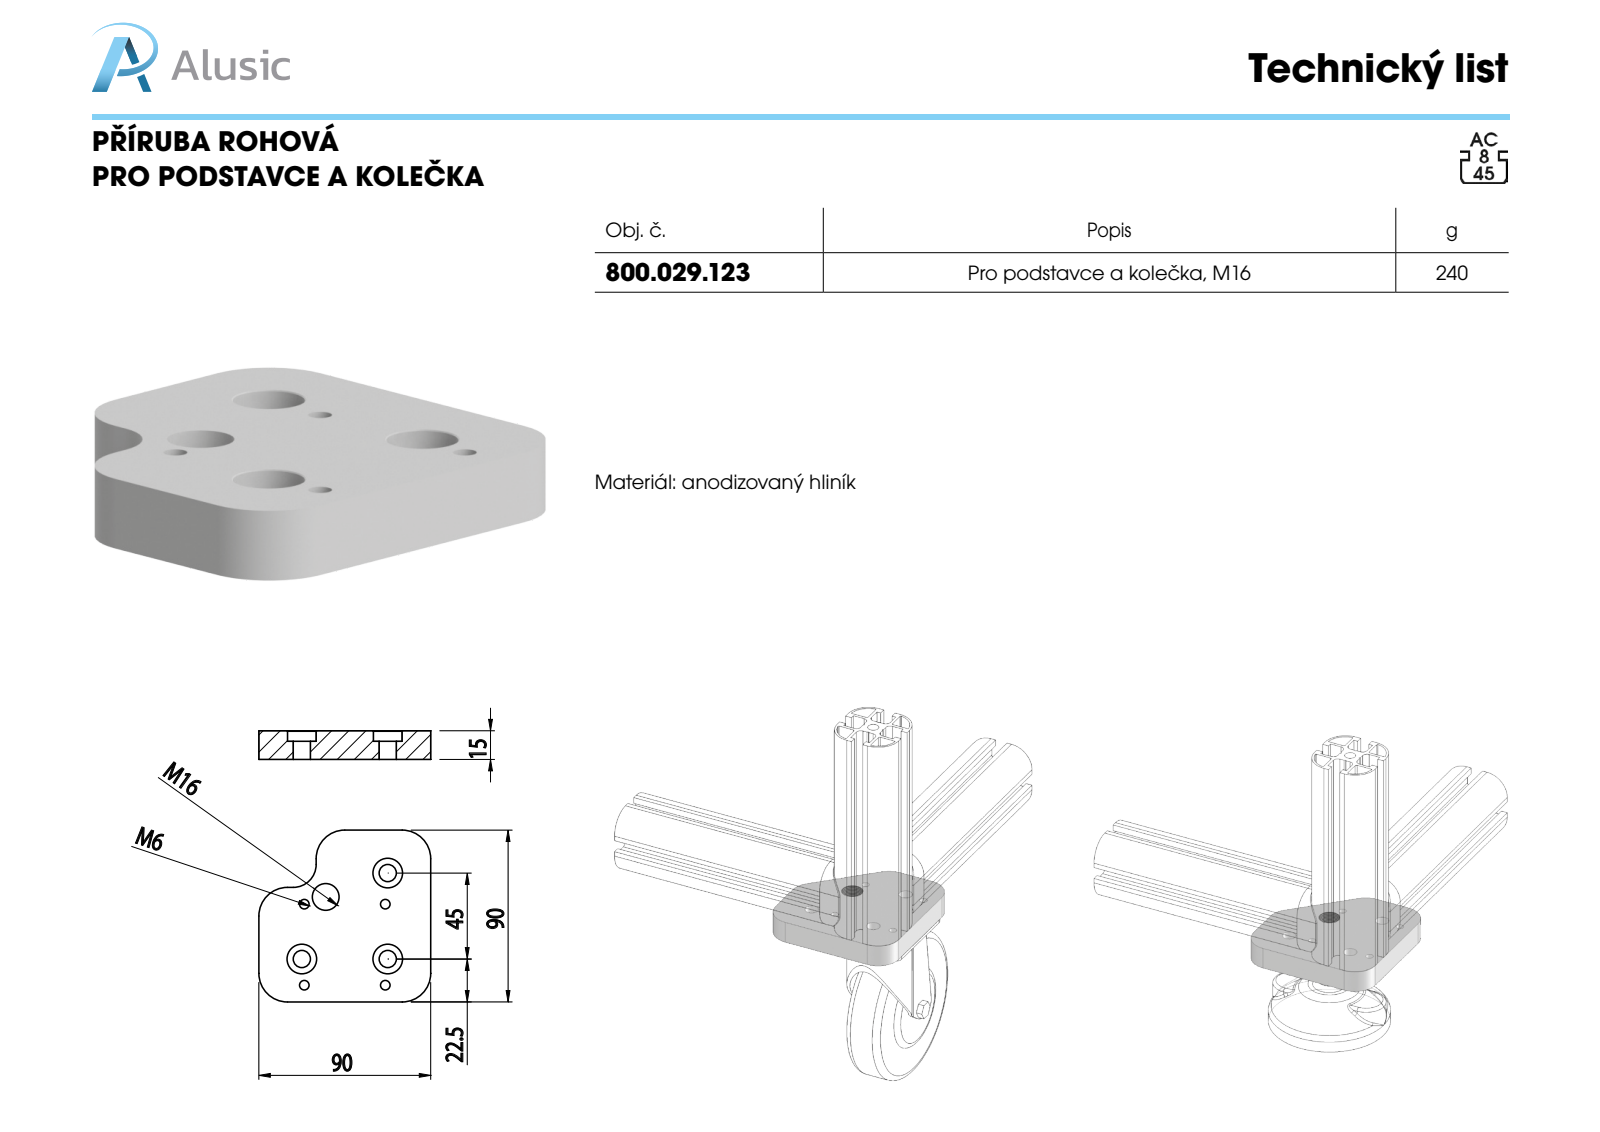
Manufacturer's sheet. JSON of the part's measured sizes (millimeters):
{"part_name": "800.029.123", "step_written_by": "SolidWorks 2011 (CONFIG_CONTROL_DESIGN)", "units": "millimeters", "bodies": {"solids": 1, "faces": 45, "planar": 11, "cylindrical": 28, "other": 6}, "overall_size": [90, 90, 15], "volume_mm3": 96622, "surface_area_mm2": 21137, "round_holes": [[5, 4], [9, 3], [15, 3], [14, 1]], "partial_cylinders_radius": [[15, 5], [12, 1]], "face_to_face_distances": [15, 90, 9.5, 5.5, 30, 60], "hole_center_spacings": [42.42, 13.77, 28.74, 34.82, 45, 45.81, 52.3, 59.99]}
